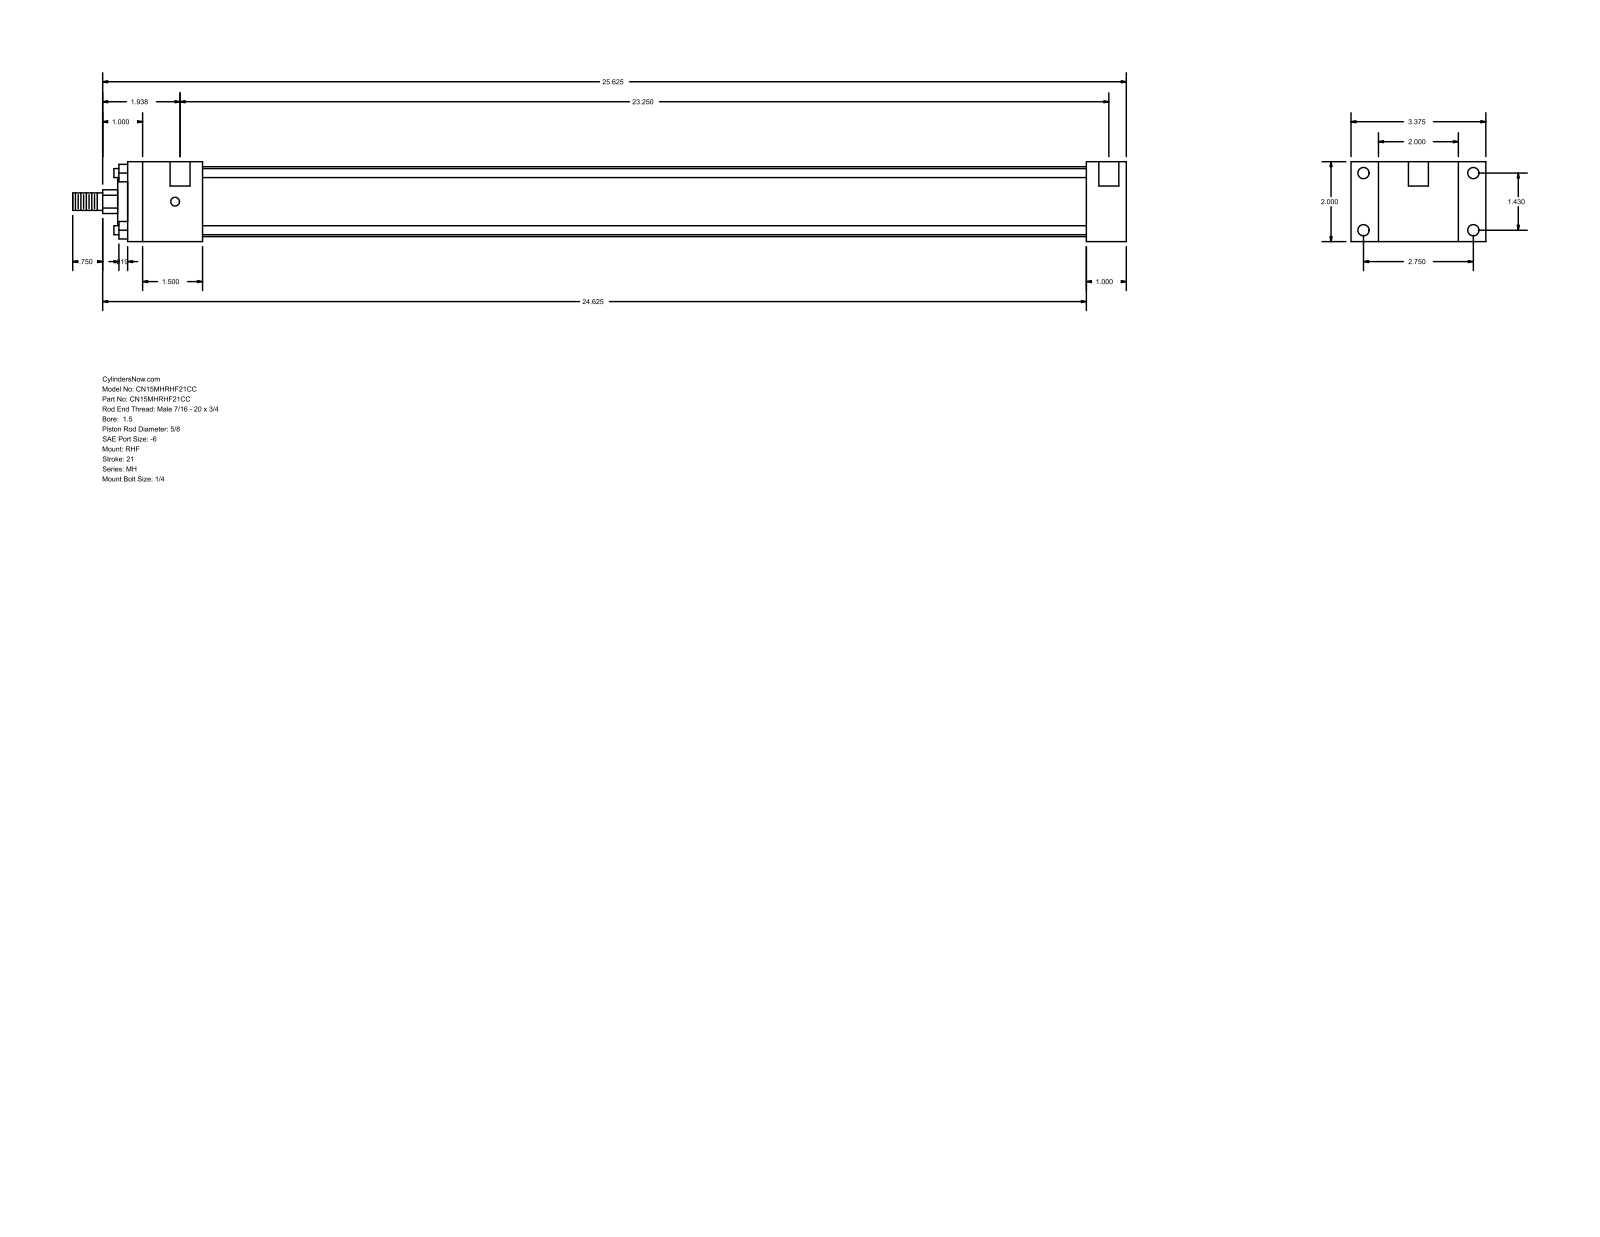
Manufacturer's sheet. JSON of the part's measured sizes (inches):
{"part_name": "MH_RHF__0150_0.625", "step_written_by": "GSSL Pune (CONFIG_CONTROL_DESIGN)", "units": "inches", "bodies": {"solids": 0, "faces": 88, "planar": 60, "cylindrical": 28, "other": 0}, "overall_size": [26.375, 3.375, 2], "round_holes": [[0.219, 4], [0.281, 4], [0.5, 2]], "round_bosses_or_shafts": [[0.225, 4], [1.75, 1], [1.125, 1], [0.625, 1], [0.437, 1]], "partial_cylinders_radius": [[0.297, 1]], "face_to_face_distances": [2, 1, 0.687, 2.687, 24, 25, 3.375, 1.875, 22.125, 23.125], "hole_center_spacings": [1.43, 2.75, 3.099, 23.375, 0.125, 23.25]}
